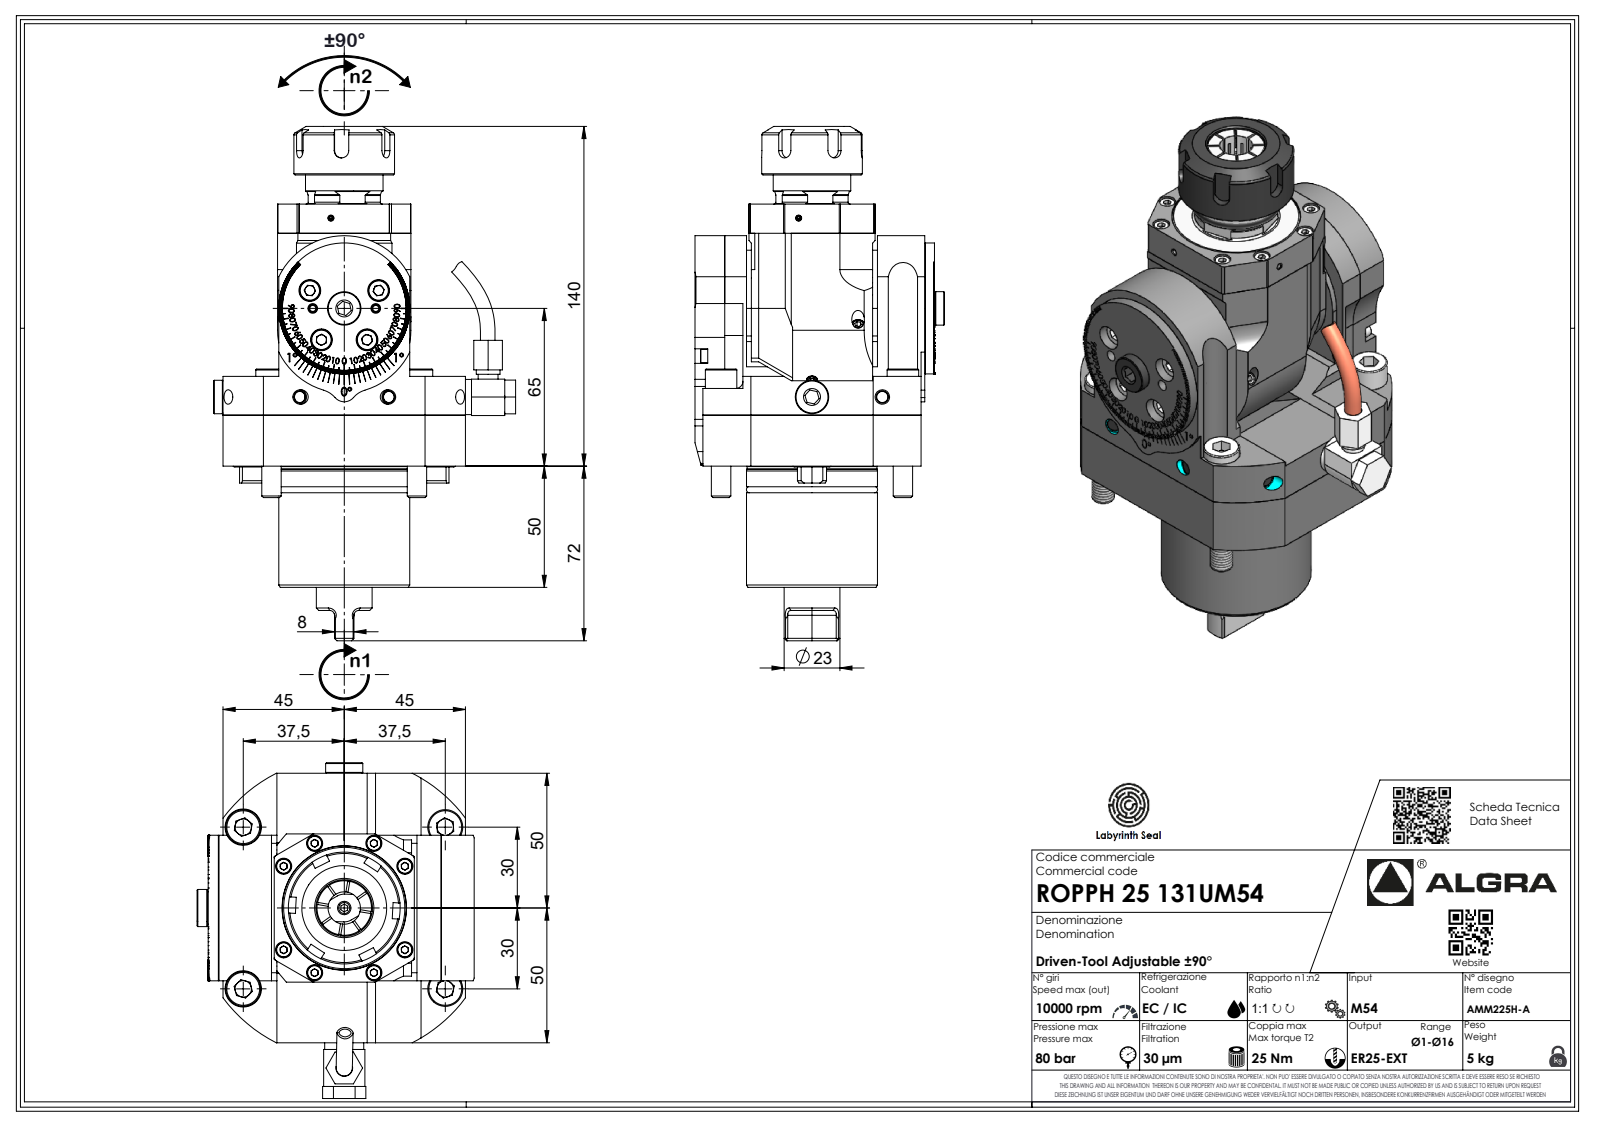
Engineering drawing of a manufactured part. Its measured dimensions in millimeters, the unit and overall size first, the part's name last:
Units: millimetres
Overall size (bounding box): 212.03 × 120.7 × 98.75
Round holes (diameter × count): ⌀2.1 ×1
Round bosses / shafts (diameter × count): ⌀54 ×2, ⌀53.6 ×1, ⌀49.9 ×1, ⌀41.5 ×1, ⌀32 ×1, ⌀23 ×1, ⌀14.5 ×1, ⌀9.8 ×1
Partial cylindrical surfaces — rounded edges, fillets, slot ends (radius × count): R1 ×8, R10 ×8, R0.33 ×7, R0.52 ×7, R3.7 ×7, R2 ×6, R3 ×6, R5 ×5
Main face-to-face distances: 0.5, 77.5, 54.5, 77, 23, 50, 71, 22.5, 98.75, 5.5
Volume: 774 828 mm³ · Surface area: 77 949 mm²
Bodies: 3 solids, 637 faces (413 planar, 118 cylindrical, 106 other)
Part name (STEP PRODUCT): ROPPH25131UM54
STEP written by: SolidWorks 2023 (AUTOMOTIVE_DESIGN)
